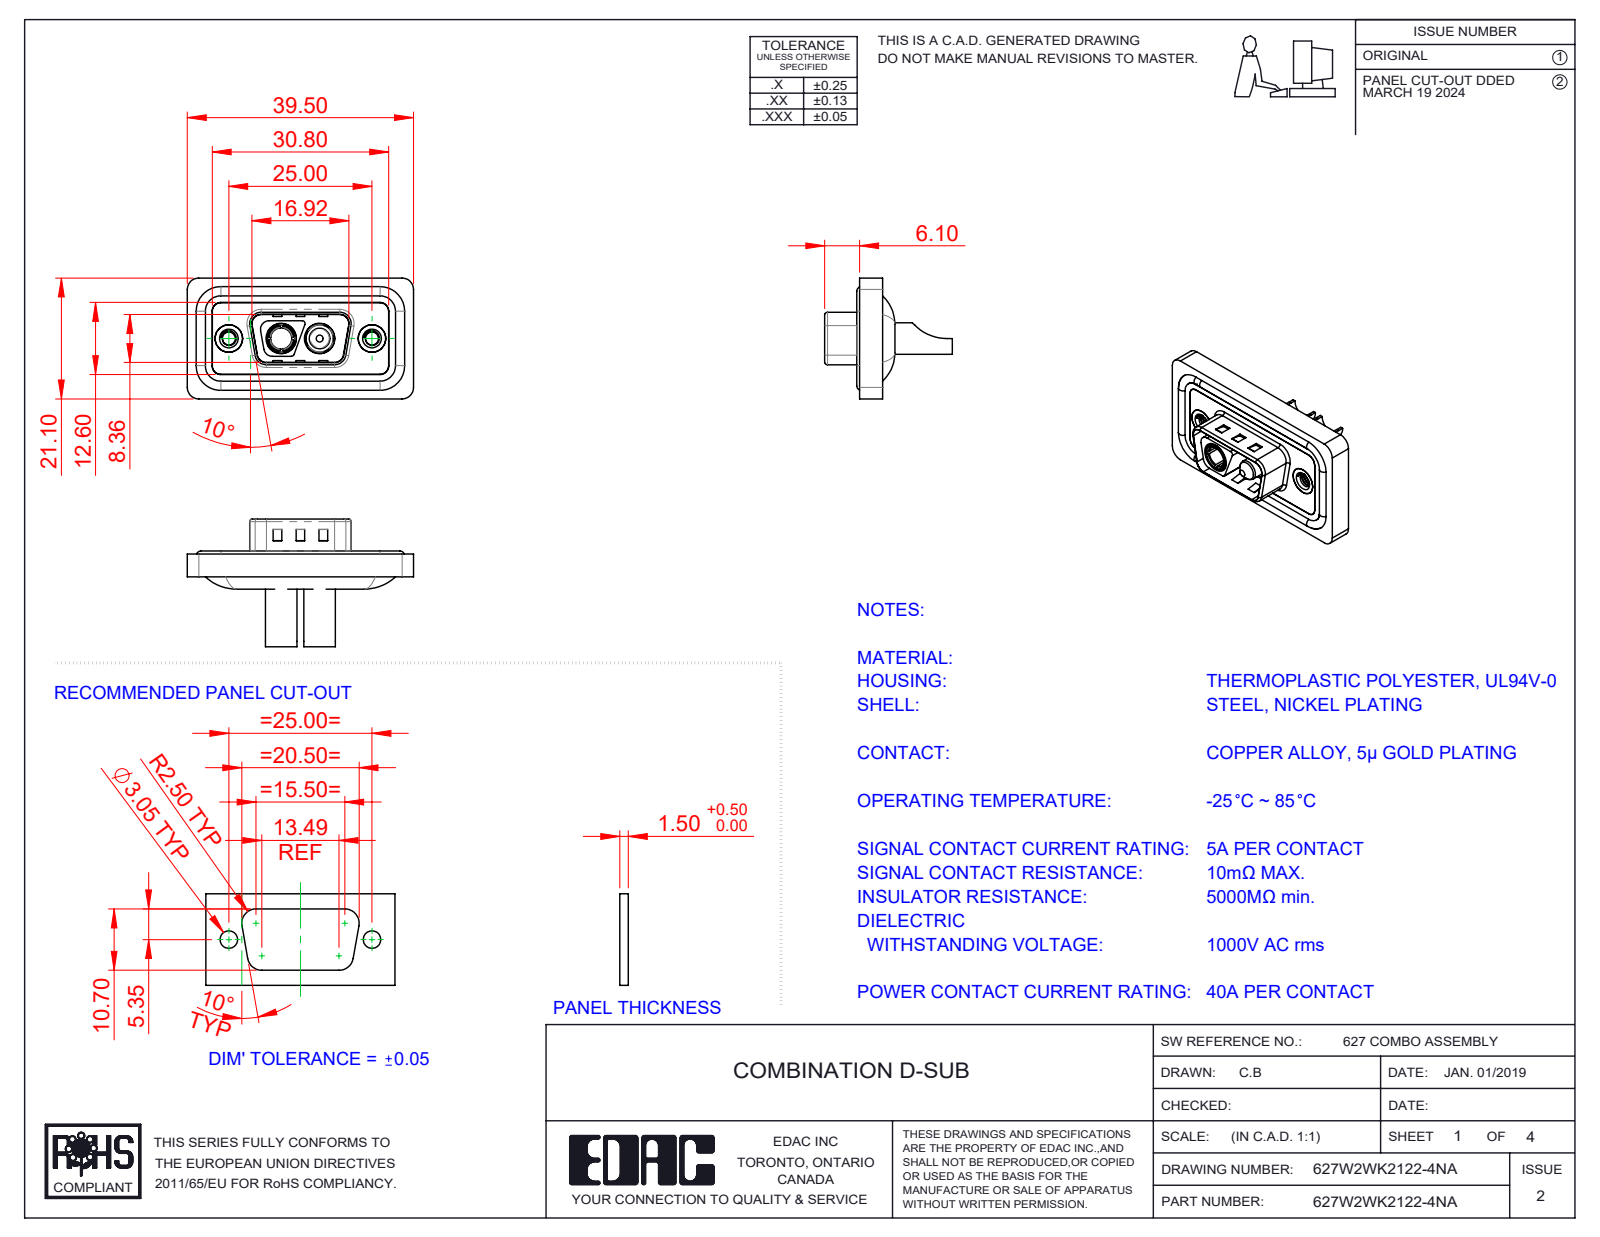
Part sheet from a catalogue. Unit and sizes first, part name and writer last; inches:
Units: inches
Overall size (bounding box): 1.555 × 0.878 × 0.831
Round holes (diameter × count): ⌀0.089 ×2, ⌀0.157 ×2, ⌀0.181 ×2, ⌀0.189 ×2, ⌀0.191 ×2, ⌀0.197 ×2, ⌀0.209 ×2, ⌀0.146 ×1
Round bosses / shafts (diameter × count): ⌀0.063 ×4, ⌀0.217 ×2, ⌀0.205 ×2, ⌀0.193 ×2, ⌀0.187 ×2, ⌀0.148 ×2, ⌀0.195 ×1, ⌀0.142 ×1
Partial cylindrical surfaces — rounded edges, fillets, slot ends (radius × count): R0.059 ×24, R0.079 ×18, R0.02 ×10, R0.063 ×8, R0.01 ×4, R0.024 ×4, R0.026 ×4, R0.035 ×4
Main face-to-face distances: 0.016, 0.043, 0.114, 0.02, 0.122, 0.063, 0.098, 0.071, 0.126, 0.059
Hole centre spacings: 0.36, 0.624, 0.265, 0.984
Volume: 0.283 in³ · Surface area: 11.81 in²
Bodies: 11 solids, 539 faces (193 planar, 231 cylindrical, 115 other)
Part name (STEP PRODUCT): Power Socket_40A SC; 627Combo Shell Front_09 Contacts; 627W2WK2122-4NA; 627Combo Shell Rear_09 Contacts (+4 more)
STEP written by: SolidWorks 2023 (CONFIG_CONTROL_DESIGN)
